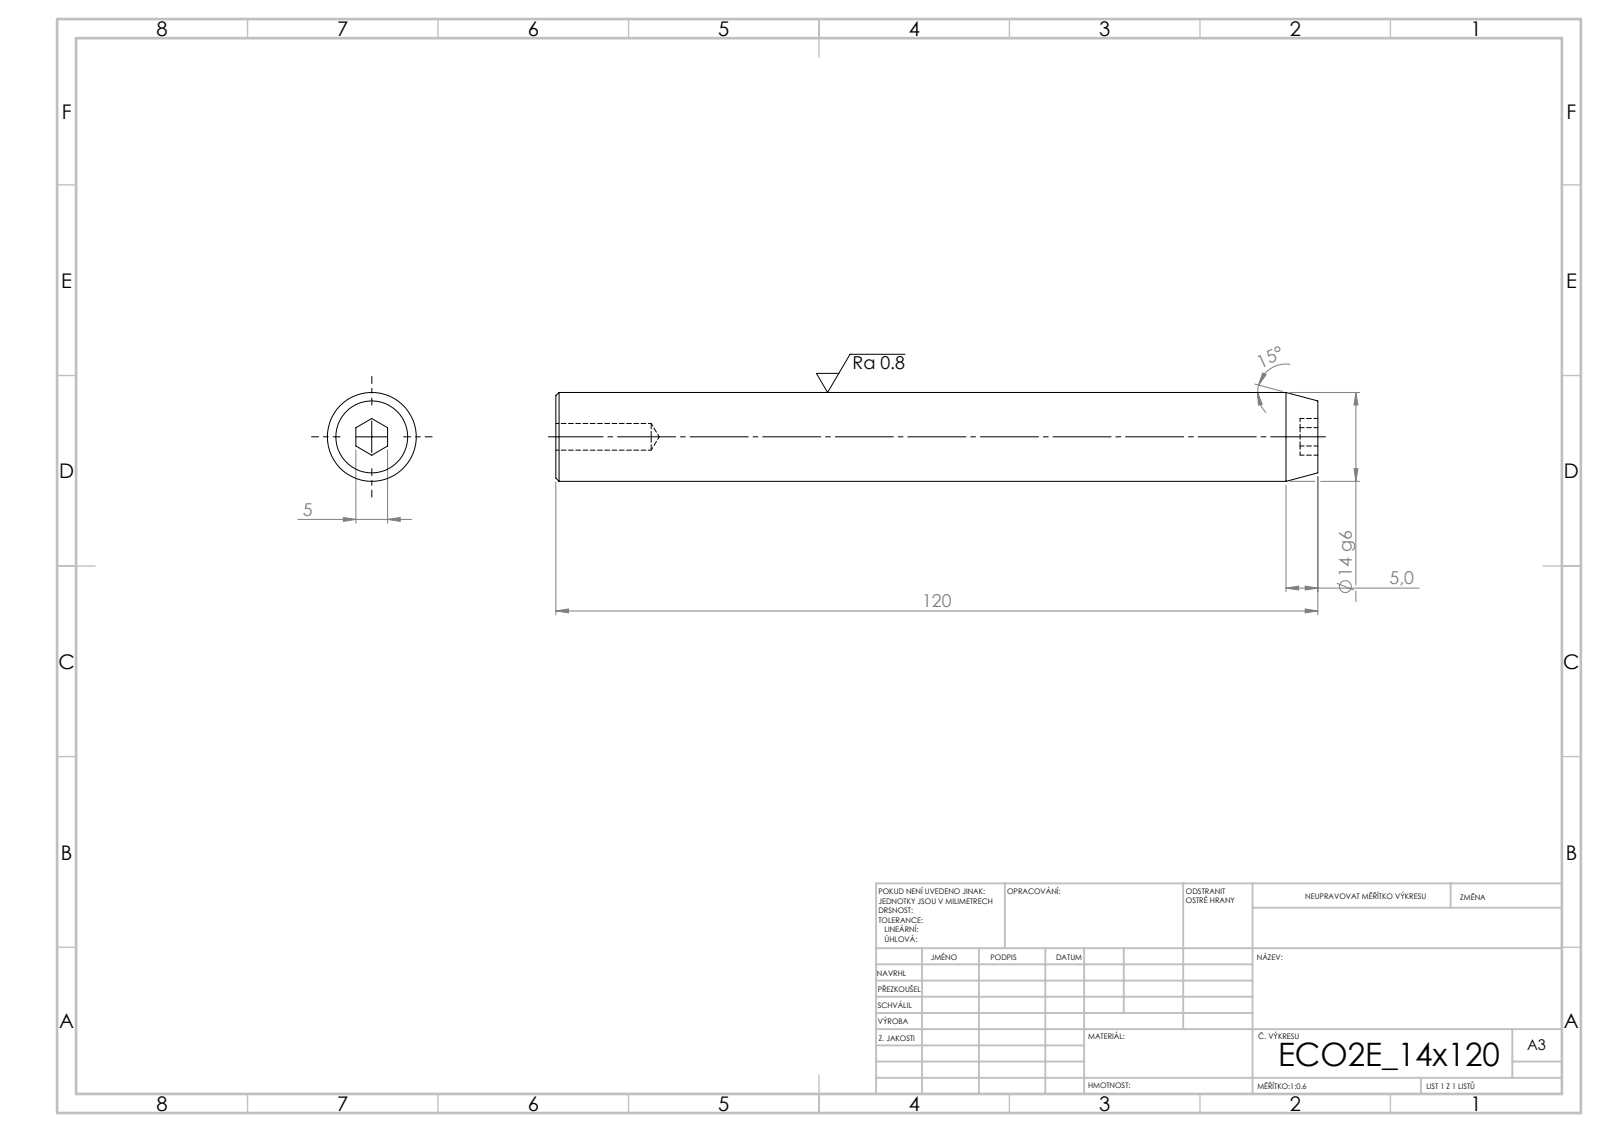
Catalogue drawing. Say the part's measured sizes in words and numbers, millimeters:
Its 3-D file was written by "SolidWorks 2019 (CONFIG_CONTROL_DESIGN)". It is 1 solid with 19 faces: 9 planar, 4 cylindrical and 6 other. Overall it measures 120 by 14 by 14 millimeters. Its volume is 18 055 cubic millimeters and its surface area 5 754 square millimeters. Round holes: 1 of diameter 4.2. Round bosses or shafts: 1 of diameter 14. The main face-to-face distances are 120, 5, 2.8, 117.2.
